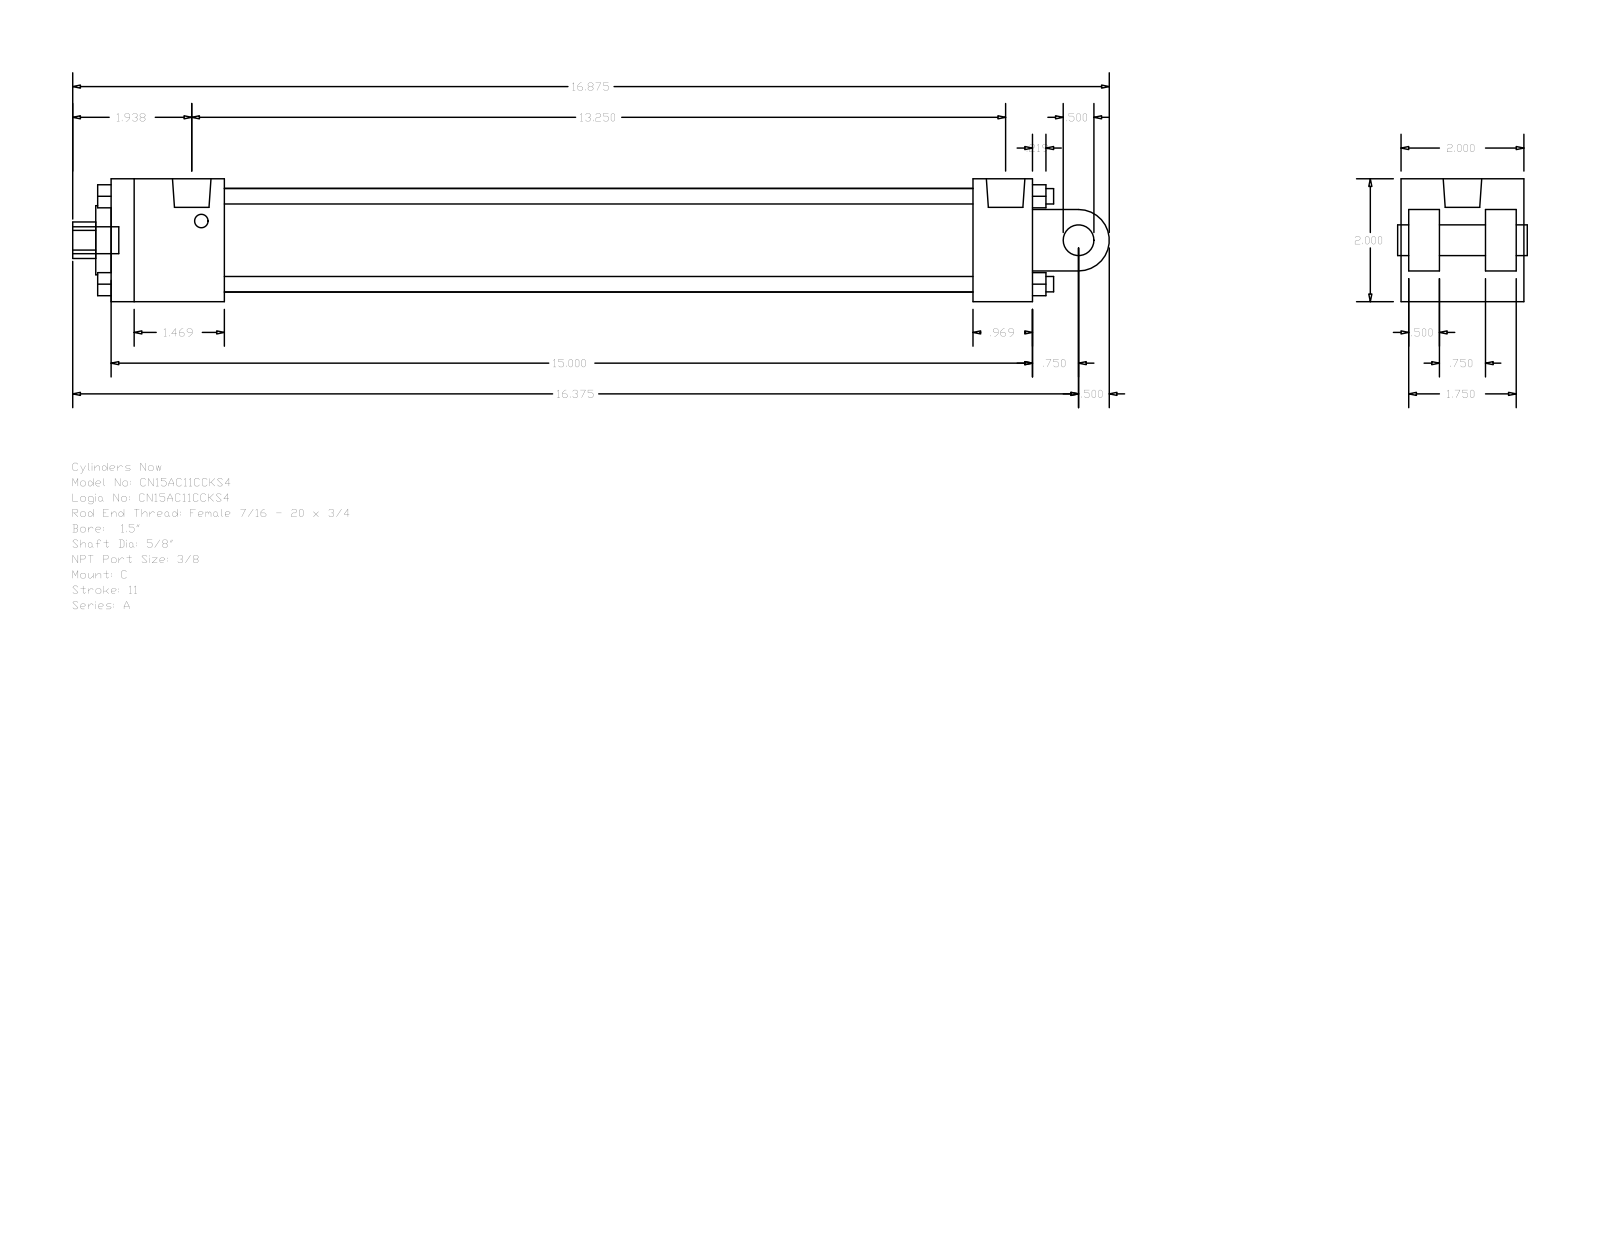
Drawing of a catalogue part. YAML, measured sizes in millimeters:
part_name: "A_C__0150_0.625"
step_written_by: "GSSL Pune (CONFIG_CONTROL_DESIGN)"
units: millimeters
bodies: {solids: 0, faces: 135, planar: 102, cylindrical: 33, other: 0}
overall_size: [428.62, 50.8, 50.8]
round_holes:
  - {diameter: 5.56, count: 2}
  - {diameter: 15.88, count: 1}
  - {diameter: 15.93, count: 1}
  - {diameter: 28.57, count: 1}
  - {diameter: 42.93, count: 1}
round_bosses_or_shafts:
  - {diameter: 6.35, count: 4}
  - {diameter: 5.56, count: 2}
  - {diameter: 15.93, count: 1}
  - {diameter: 12.7, count: 1}
  - {diameter: 11.11, count: 1}
partial_cylinders:
  - {radius: 7.54, count: 1}
  - {radius: 12.7, count: 1}
face_to_face_distances: [50.8, 12.7, 381, 3.17, 15.87, 34.93, 47.63, 31.76, 356.39, 24.61]
hole_center_spacings: [3.97]
